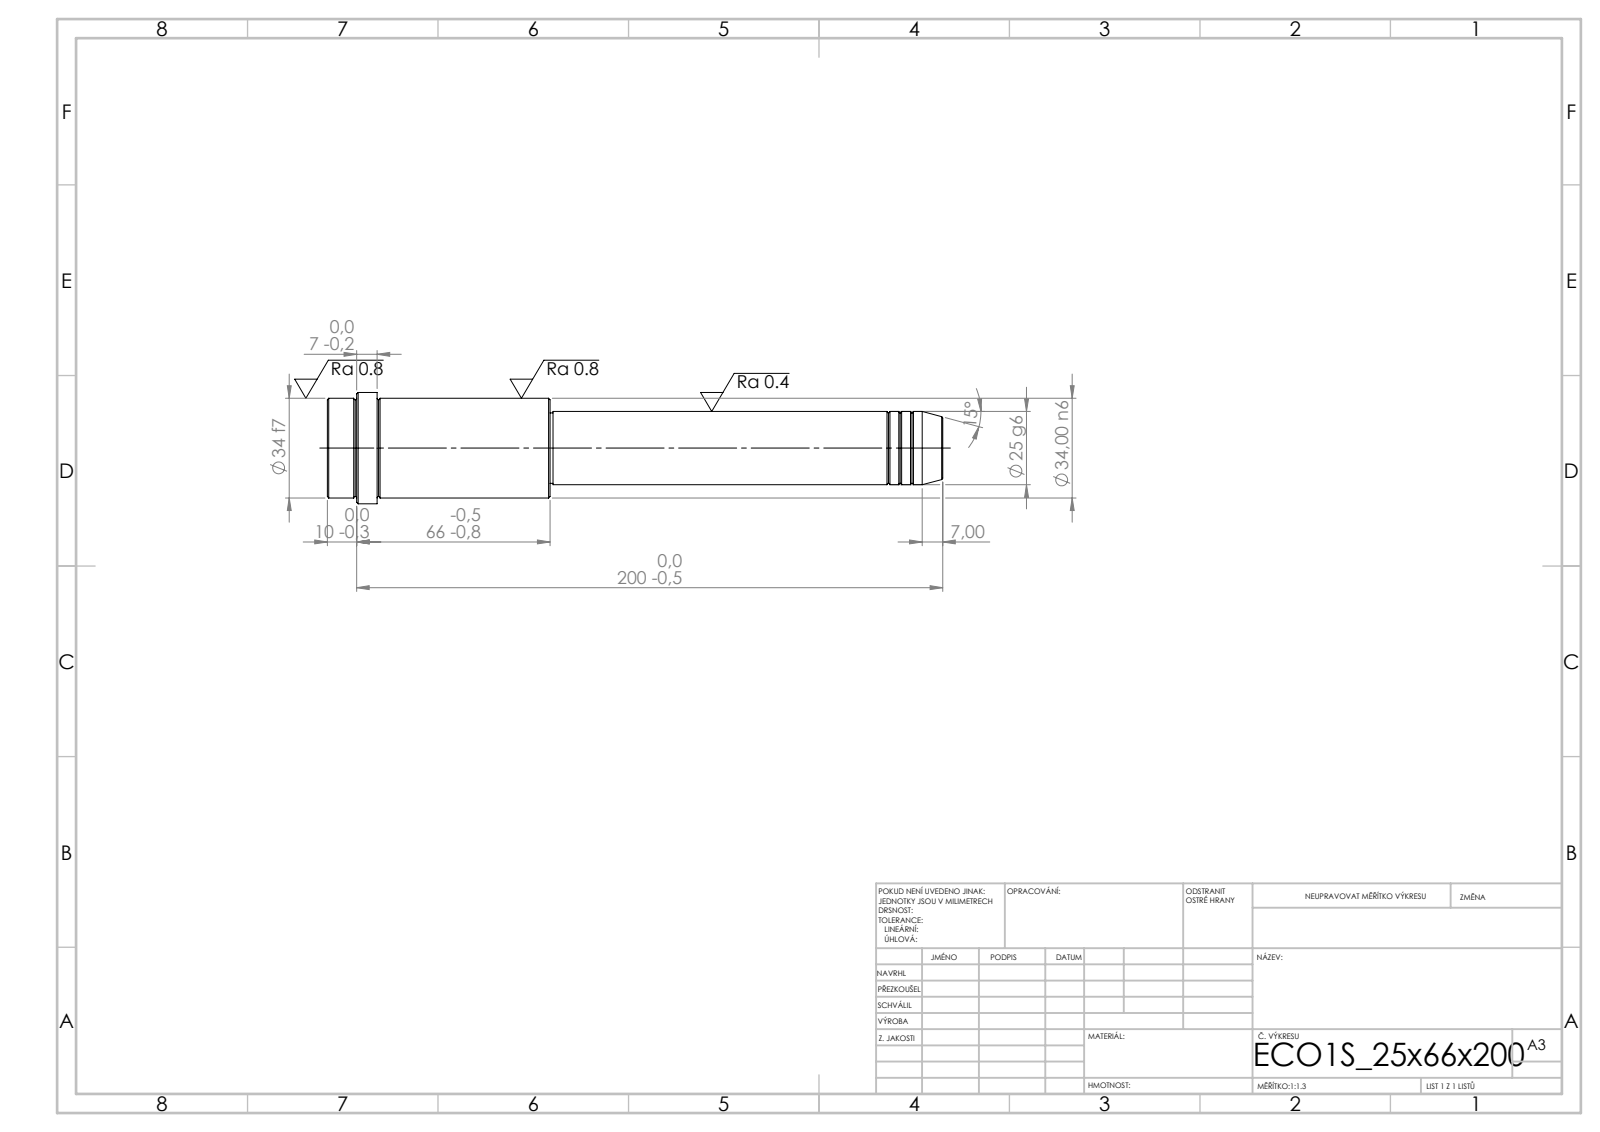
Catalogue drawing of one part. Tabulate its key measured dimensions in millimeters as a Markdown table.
| quantity | value |
| --- | --- |
| STEP written by | SolidWorks 2019 (CONFIG_CONTROL_DESIGN) |
| units | millimeters |
| bodies | 1 solid, 52 faces (6 planar, 16 cylindrical, 30 other) |
| overall size | 210 × 38 × 38 |
| volume | 135 617 mm³ |
| surface area | 21 047 mm² |
| round bosses / shafts (diameter × count) | 38 × 1, 34 × 1, 25 × 1, 24 × 1 |
| main face-to-face distances | 76, 134, 210, 193, 59, 17, 200, 66, 7, 10 |
